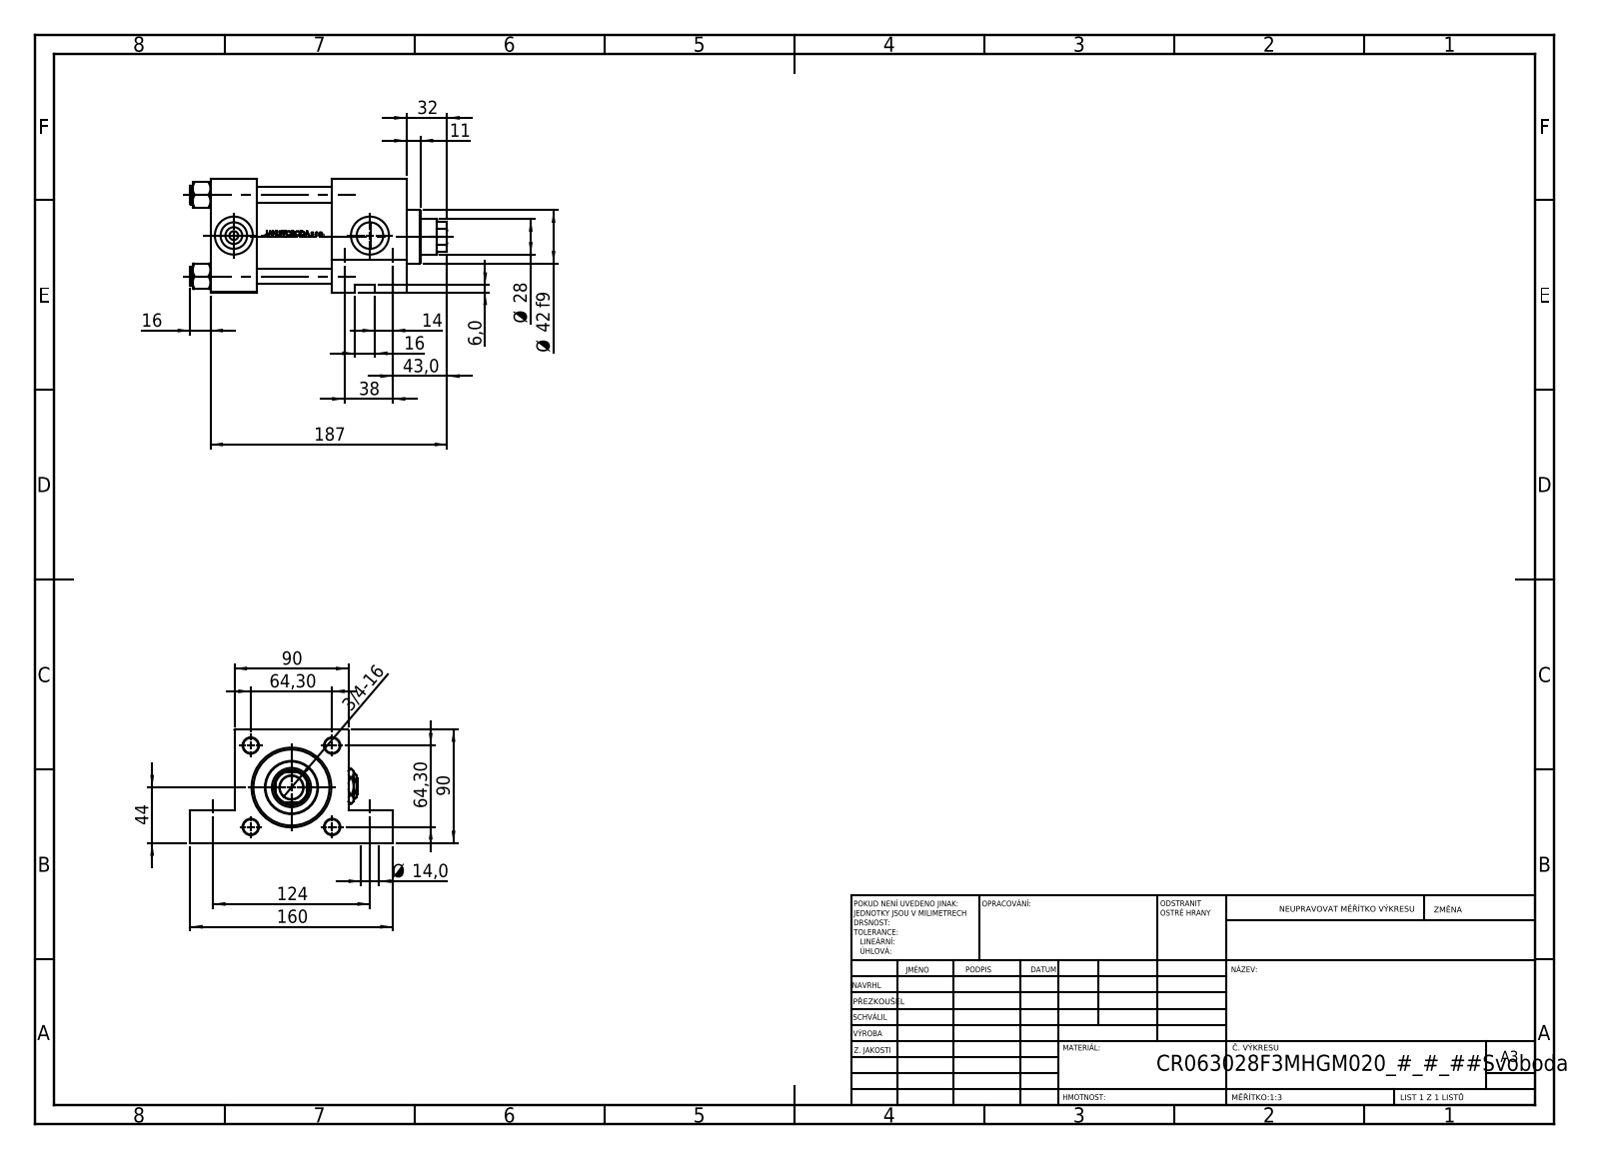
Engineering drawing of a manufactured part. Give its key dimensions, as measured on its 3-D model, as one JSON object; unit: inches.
{"part_name": "V215_VC_A; V215CR_VCP_F; V215CR_F_TYCINKA; V215CR_F_Body (+2 more)", "step_written_by": "SolidWorks 2019 (CONFIG_CONTROL_DESIGN)", "units": "inches", "bodies": {"solids": 13, "faces": 1200, "planar": 484, "cylindrical": 134, "other": 582}, "overall_size": [7.992, 6.299, 3.543], "volume_in3": 62.43, "surface_area_in2": 307.9, "round_holes": [[0.472, 4], [0.825, 3], [1.181, 3], [0.276, 2], [0.551, 2], [0.551, 2], [0.728, 1], [0.787, 1], [1.102, 1], [1.22, 1], [1.969, 1], [2.362, 1]], "round_bosses_or_shafts": [[0.591, 4], [2.717, 1], [1.654, 1]], "partial_cylinders_radius": [[0.531, 1]], "face_to_face_distances": [3.543, 2.323, 1.457, 4.646, 6.102, 3.78, 0.787, 1.024, 2.52, 4.921], "hole_center_spacings": [2.531, 1.496, 1.763, 1.818, 3.58, 4.882, 5.106, 0.394]}
